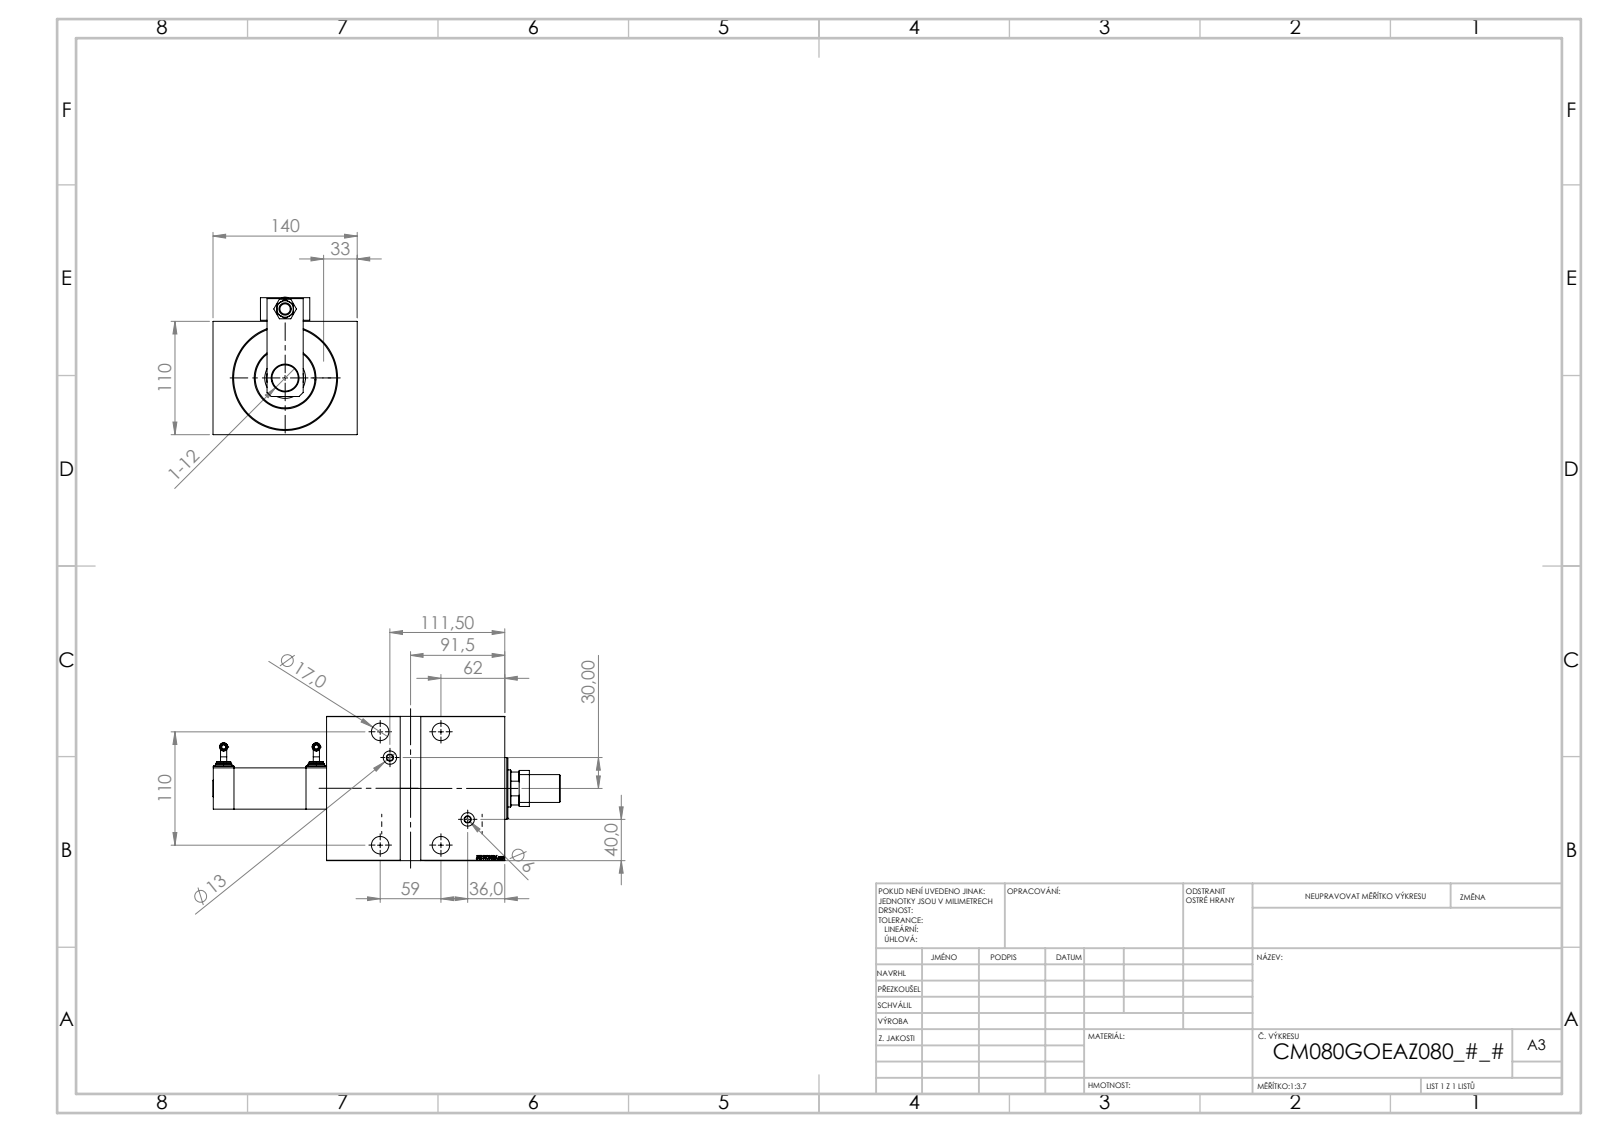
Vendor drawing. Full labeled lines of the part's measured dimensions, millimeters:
Part name (STEP PRODUCT): NUT_D19_P; SWITCH_P_FRONT_BACK; TYC_P; SWITCH DIM W_B (+8 more)
STEP written by: SolidWorks 2019 (CONFIG_CONTROL_DESIGN)
Units: millimetres
Bodies: 17 solids, 1163 faces (562 planar, 126 cylindrical, 475 other)
Overall size (bounding box): 337.3 × 140 × 133.5
Volume: 2 480 000 mm³ · Surface area: 312 077 mm²
Round holes (diameter × count): ⌀4 ×4, ⌀8 ×4, ⌀17 ×4, ⌀25 ×4, ⌀13 ×3, ⌀6 ×2, ⌀12 ×1, ⌀14 ×1, ⌀25.5 ×1, ⌀27 ×1, ⌀36 ×1, ⌀39.5 ×1
Round bosses / shafts (diameter × count): ⌀20 ×3, ⌀26 ×2, ⌀16 ×2, ⌀14 ×2, ⌀8 ×2, ⌀7 ×2, ⌀6 ×2, ⌀5.04 ×2
Partial cylindrical surfaces — rounded edges, fillets, slot ends (radius × count): R3 ×1, R17.5 ×1
Main face-to-face distances: 110, 140, 173, 5, 21, 90, 152, 168, 147, 50
Hole centre spacings: 20, 59, 63.29, 70.68, 78.77, 84.82, 110, 112.86
